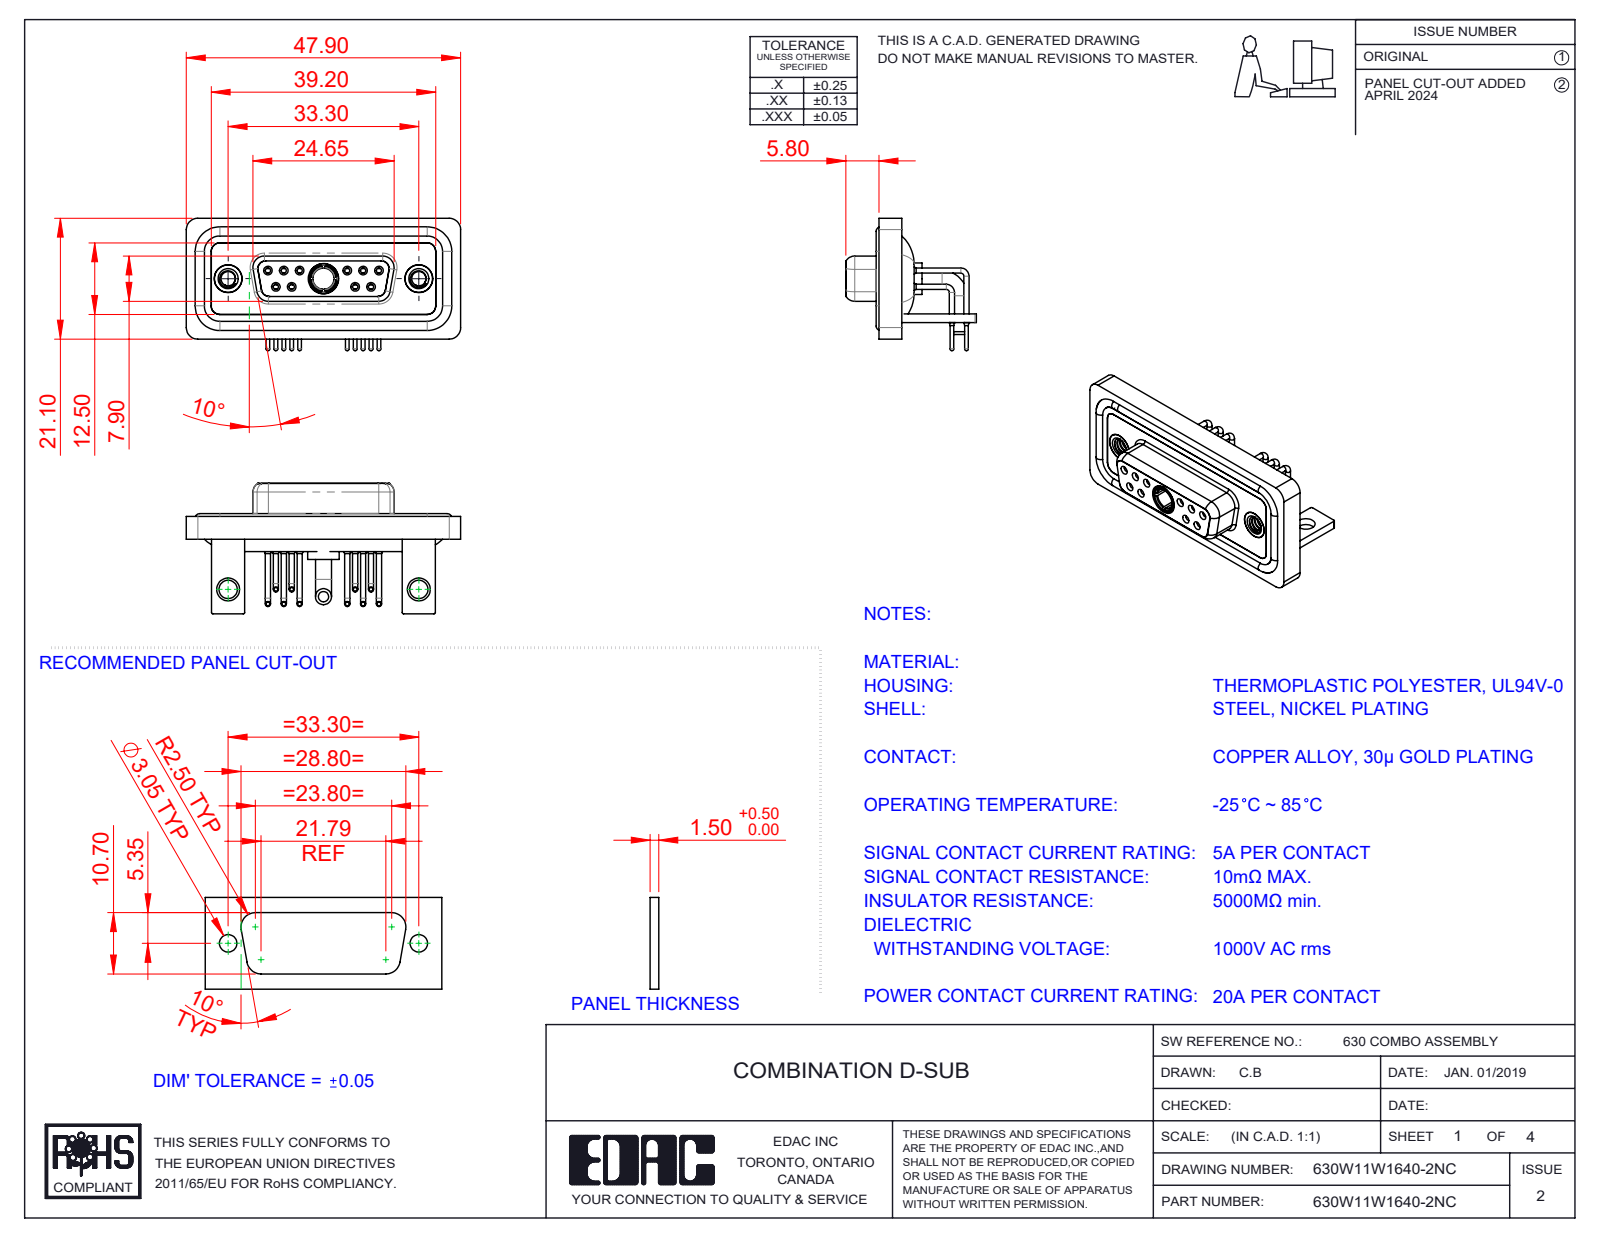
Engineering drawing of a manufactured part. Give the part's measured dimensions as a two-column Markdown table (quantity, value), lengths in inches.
| quantity | value |
| --- | --- |
| part name | 630Combo Waterproof Housing_15 Contacts; 630Combo Shell Front_15 Contacts; 630Combo Stabilizer Bracket_50 Contacts; 630Combo Contact Row 1_50 Contacts (+6 more) |
| STEP written by | SolidWorks 2023 (CONFIG_CONTROL_DESIGN) |
| units | inches |
| bodies | 21 solids, 1036 faces (304 planar, 465 cylindrical, 267 other) |
| overall size | 1.886 × 0.91 × 0.898 |
| volume | 0.401 in³ |
| surface area | 17.37 in² |
| round holes (diameter × count) | 0.035 × 10, 0.043 × 10, 0.059 × 10, 0.079 × 10, 0.067 × 6, 0.063 × 4, 0.191 × 3, 0.098 × 2, 0.126 × 2, 0.157 × 2, 0.159 × 2, 0.197 × 2 |
| round bosses / shafts (diameter × count) | 0.063 × 10, 0.035 × 10, 0.026 × 10, 0.195 × 2, 0.189 × 2, 0.11 × 2, 0.217 × 1, 0.205 × 1 |
| partial cylindrical surfaces (radius × count) | 0.079 × 21, 0.059 × 18, 0.01 × 16, 0.053 × 12, 0.063 × 8, 0.02 × 5, 0.024 × 4, 0.026 × 4 |
| main face-to-face distances | 0.016, 0.114, 0.071, 0.059, 0.146, 0.043, 0.063, 0.161, 0.031, 0.098 |
| hole center spacings | 0.124, 0.109, 0.545, 0.436, 0.654, 0.198, 0.198, 0.218 |
